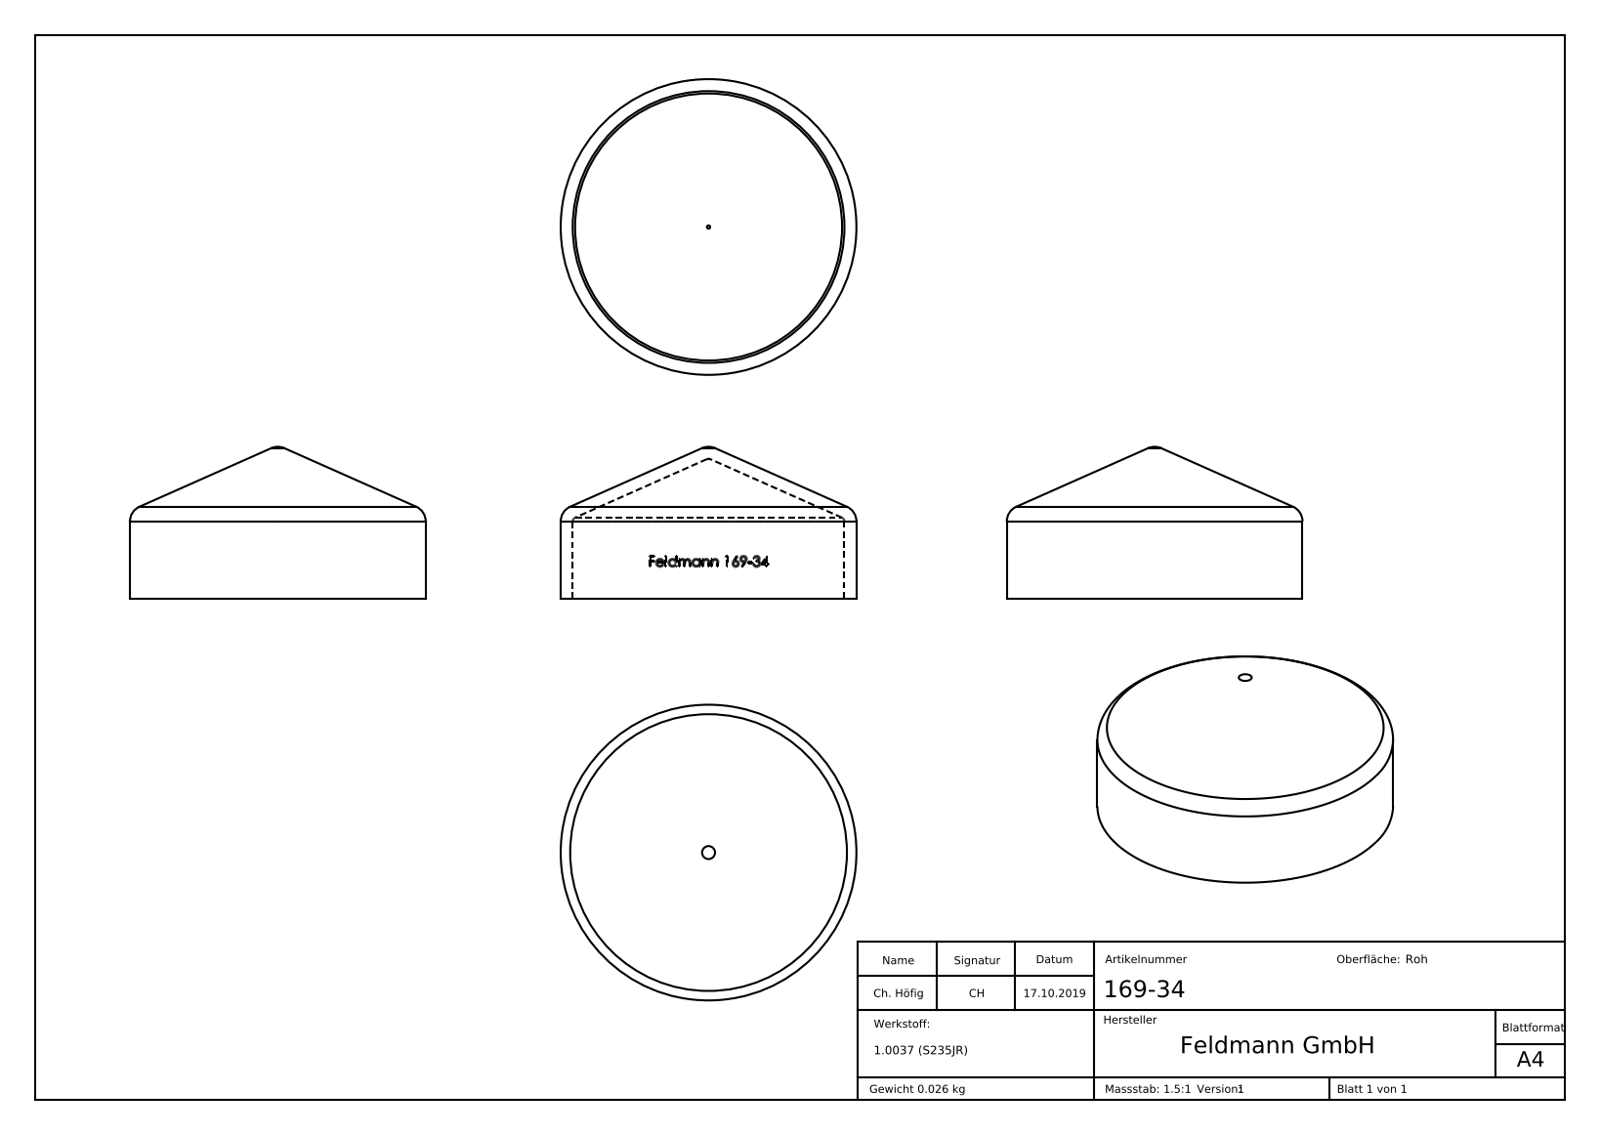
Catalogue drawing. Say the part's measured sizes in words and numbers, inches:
The part is named "169-34". Its 3-D file was written by "SolidWorks 2015 (CONFIG_CONTROL_DESIGN)". It is 1 solid with 195 faces: 87 planar, 22 cylindrical and 86 other. Overall it measures 1.457 by 1.457 by 0.748 inches. Its volume is 0.204 cubic inches and its surface area 7.2 square inches. Round holes: 1 of diameter 1.339. Round bosses or shafts: 1 of diameter 1.457. Partial cylindrical surfaces (rounded edges, fillets, slot ends): 1 of radius 0.673. The main face-to-face distances are 0.015, 0.08, 0.496, 0.05, 0.575, 0.446, 0.065, 0.117, 0.117, 0.052.
